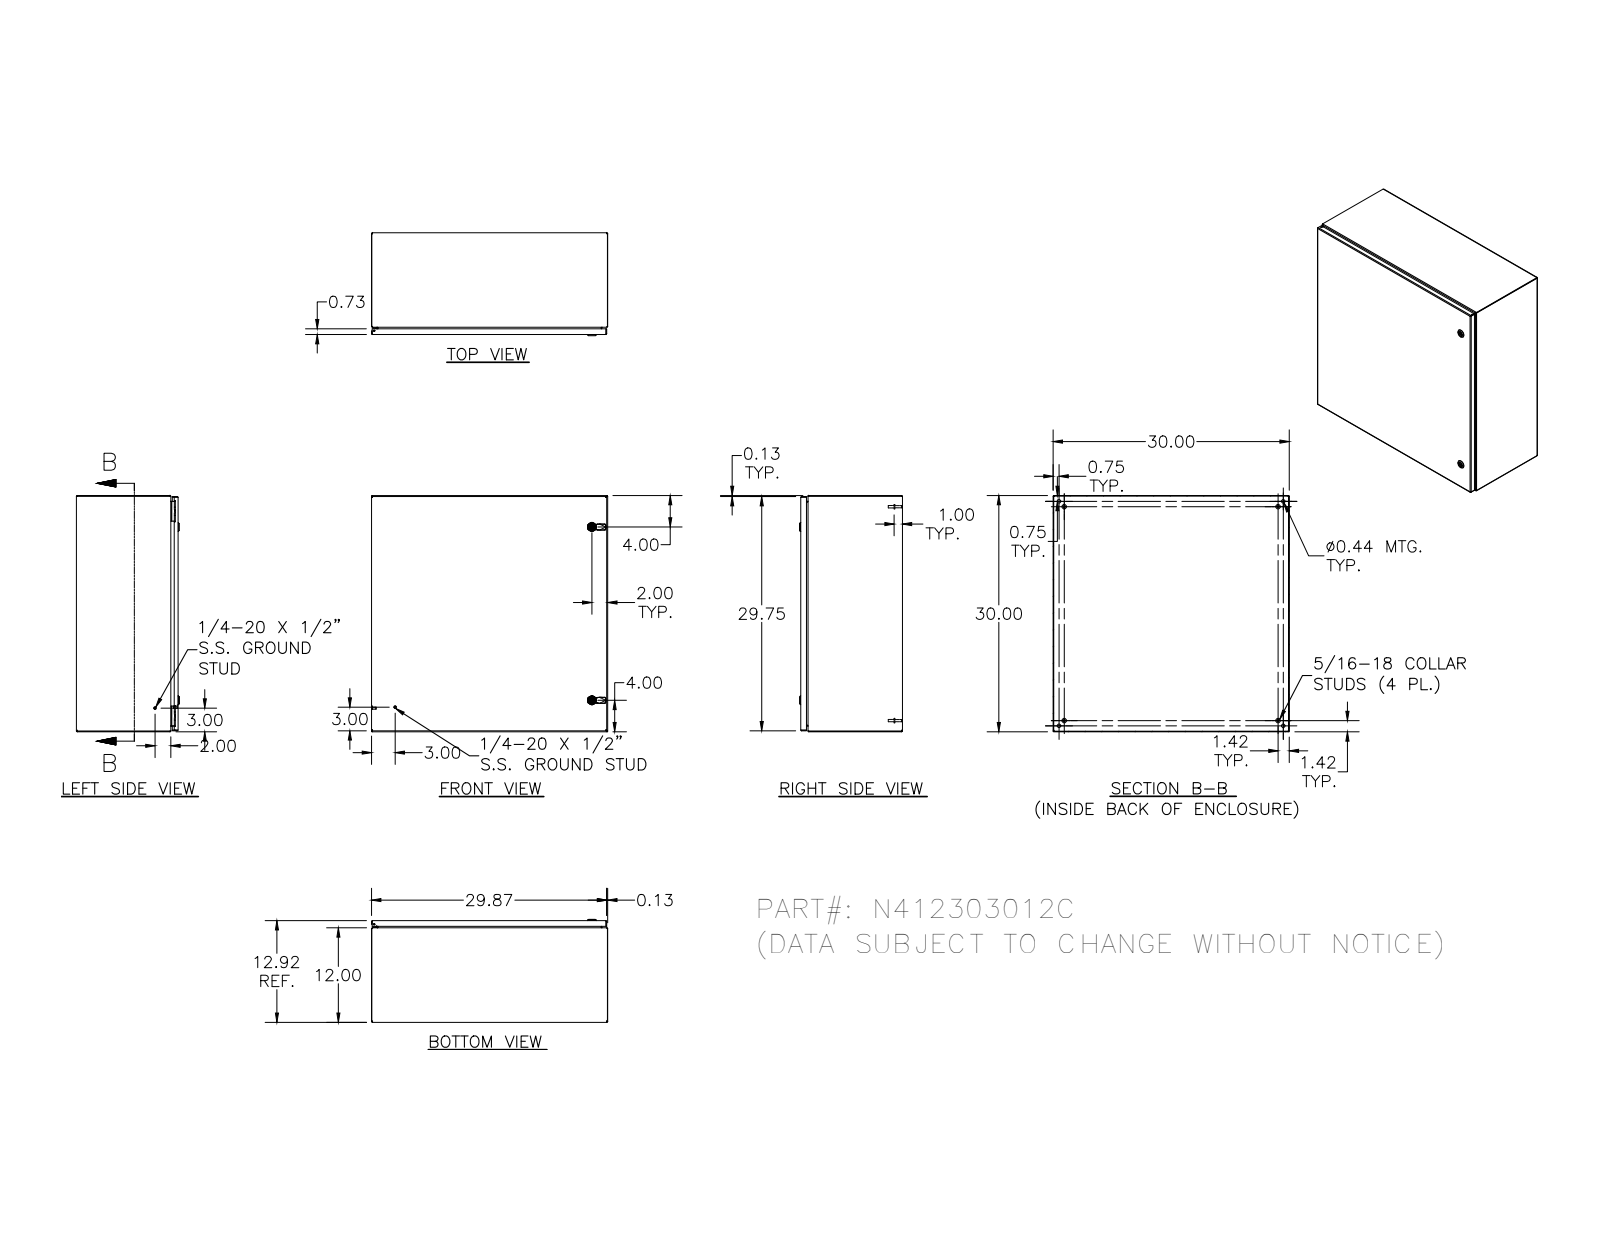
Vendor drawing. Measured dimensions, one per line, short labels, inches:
name: N412303012C; N4123030CLID; 35124; 1000-u155_asm (+8 more)
written by: Autodesk Inventor 2011 (AUTOMOTIVE_DESIGN)
unit: in
bodies: 38 solids, 1816 faces (706 planar, 678 cylindrical, 432 other)
size: 30 × 30 × 13.075
volume: 257.1 in³; area: 6 989 in²
holes: 5× ⌀0.188, 4× ⌀0.093, 4× ⌀0.152, 4× ⌀0.167, 4× ⌀0.172, 4× ⌀0.437, 2× ⌀0.156, 2× ⌀0.197, 2× ⌀0.315, 2× ⌀0.394, 2× ⌀0.402, 2× ⌀0.634
bosses: 10× ⌀0.25, 4× ⌀0.563, 4× ⌀0.36, 4× ⌀0.32, 4× ⌀0.3, 4× ⌀0.275, 4× ⌀0.256, 4× ⌀0.164
rounds: 54× R0.012, 30× R0.031, 26× R0.05, 23× R0.02, 20× R0.105, 18× R0.016, 16× R0.125, 8× R0.032
face distances: 0.074, 12.843, 12.769, 12.917, 0.074, 29.926, 29.852, 29.926, 30, 0.917
hole spacings: 26, 0.66, 28.5, 0.656, 1.307, 1.965, 0.5, 0.984
